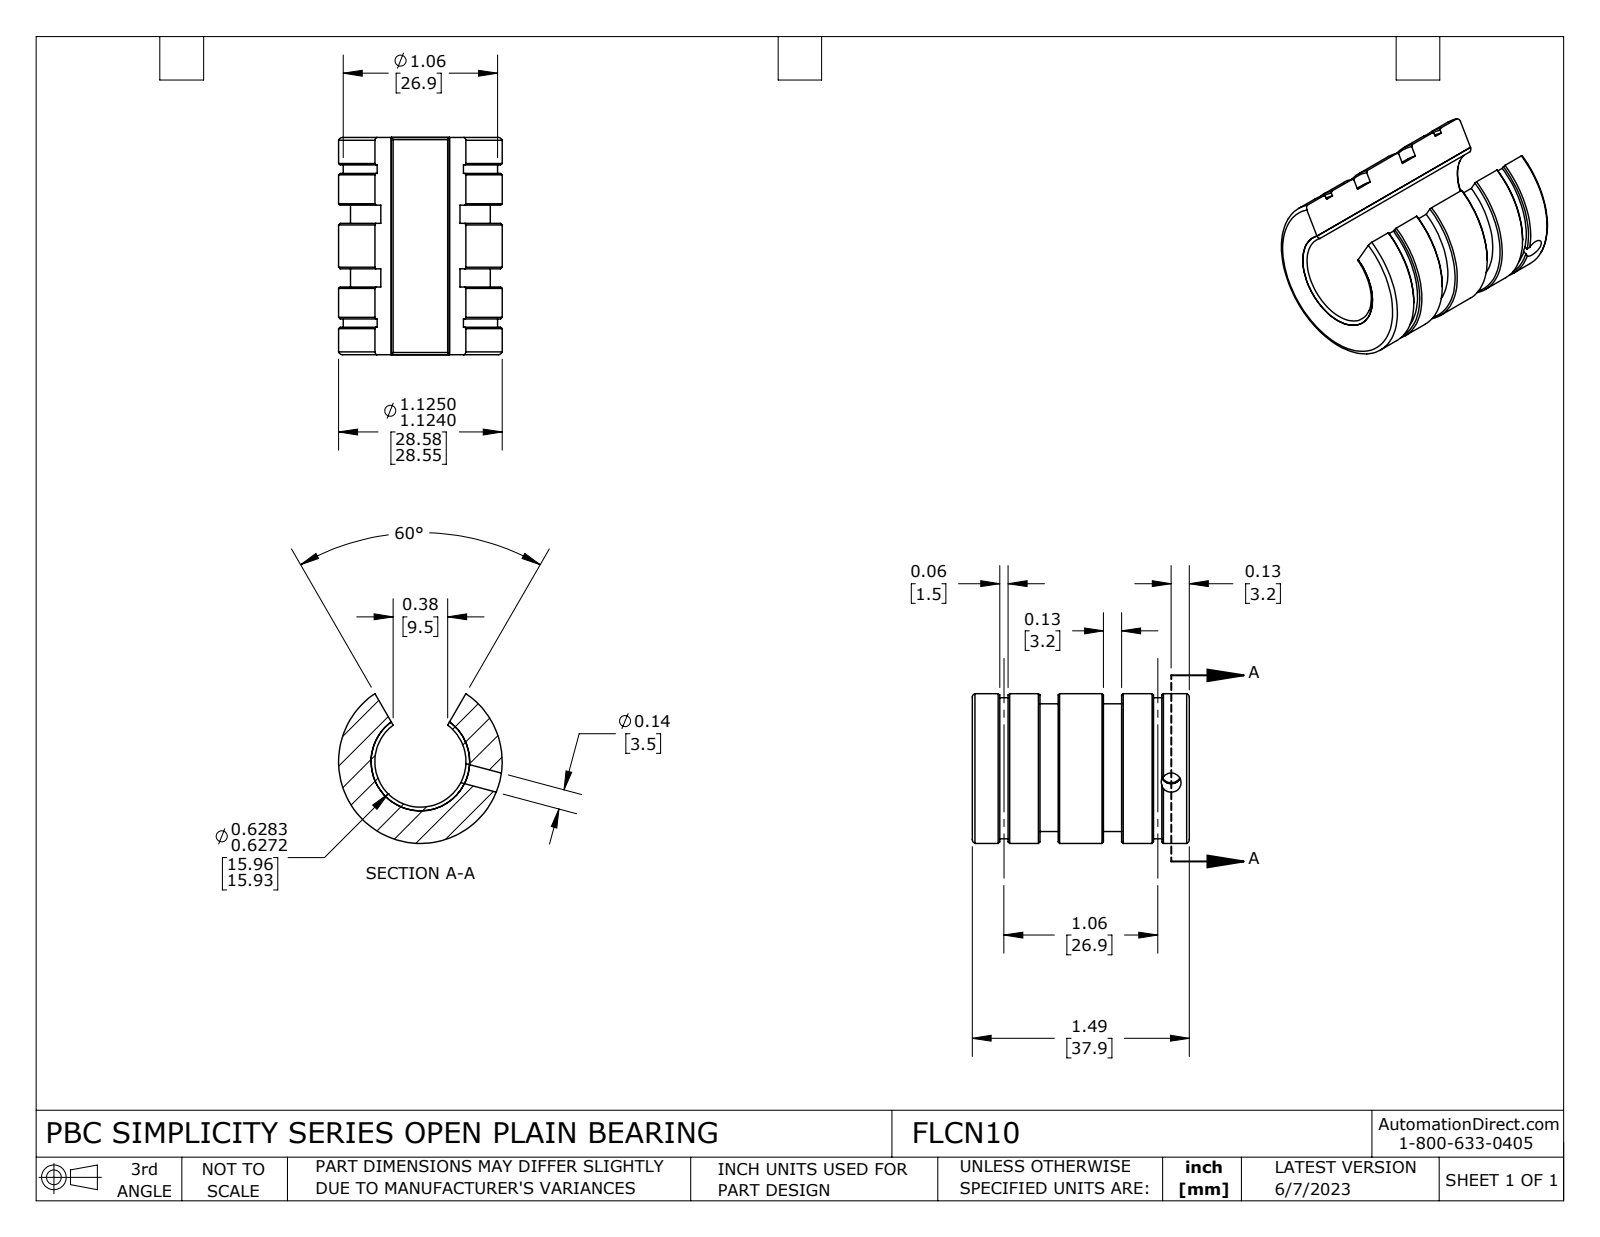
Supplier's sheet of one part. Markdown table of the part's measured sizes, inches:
| quantity | value |
| --- | --- |
| part name | FLCN10 |
| STEP written by | SolidWorks 2021 (CONFIG_CONTROL_DESIGN) |
| units | inches |
| bodies | 2 solids, 83 faces (15 planar, 40 cylindrical, 28 other) |
| overall size | 1.493 × 1.124 × 1.029 |
| volume | 0.754 in³ |
| surface area | 14.39 in² |
| round holes (diameter × count) | 0.136 × 1, 0.626 × 1, 0.677 × 1 |
| round bosses / shafts (diameter × count) | 1.124 × 1, 1.06 × 1, 0.962 × 1 |
| main face-to-face distances | 1.492, 0.59, 0.902, 0.465, 1.027, 0.125, 0.437, 0.312, 0.562, 0.246 |
